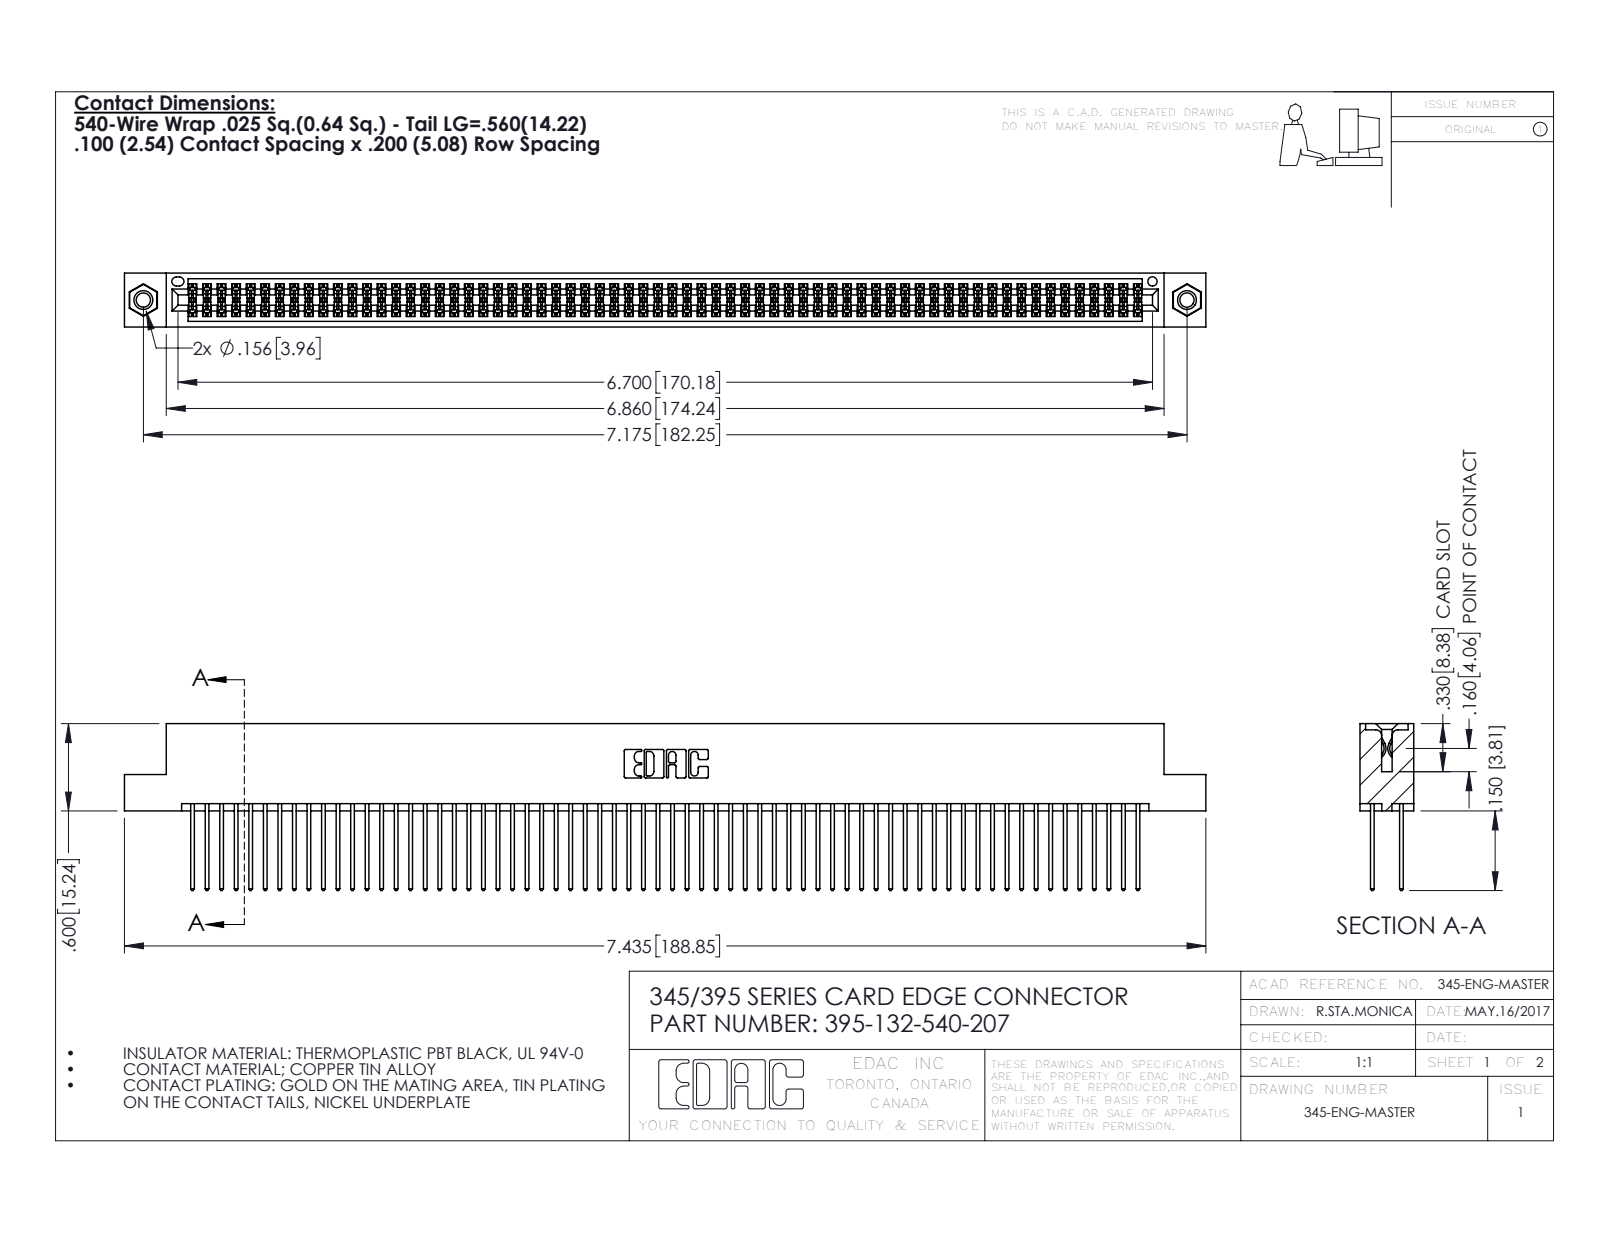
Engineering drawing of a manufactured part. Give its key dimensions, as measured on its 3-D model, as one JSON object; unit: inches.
{"part_name": "345-292-001_345-293-140; 395-132-540-207; 345 Part_Flush Mounting Lugs - 0.156 Dia-TI; 345-250-001_345-250-005-103", "step_written_by": "SolidWorks 2016 (CONFIG_CONTROL_DESIGN)", "units": "inches", "bodies": {"solids": 135, "faces": 6786, "planar": 4468, "cylindrical": 2302, "other": 16}, "overall_size": [7.435, 1.147, 0.37], "volume_in3": 1.163, "surface_area_in2": 48.02, "round_holes": [[0.098, 2], [0.125, 2], [0.156, 2], [0.064, 1]], "round_bosses_or_shafts": [[0.155, 2]], "partial_cylinders_radius": [[0.006, 198], [0.01, 132], [0.01, 22], [0.007, 6], [0.031, 6], [0.026, 3], [0.014, 2], [0.019, 2]], "face_to_face_distances": [0.072, 0.298, 0.2, 0.098, 0.272, 0.025, 0.225, 0.37, 0.175, 0.149], "hole_center_spacings": [0.27, 6.939, 7.175]}
